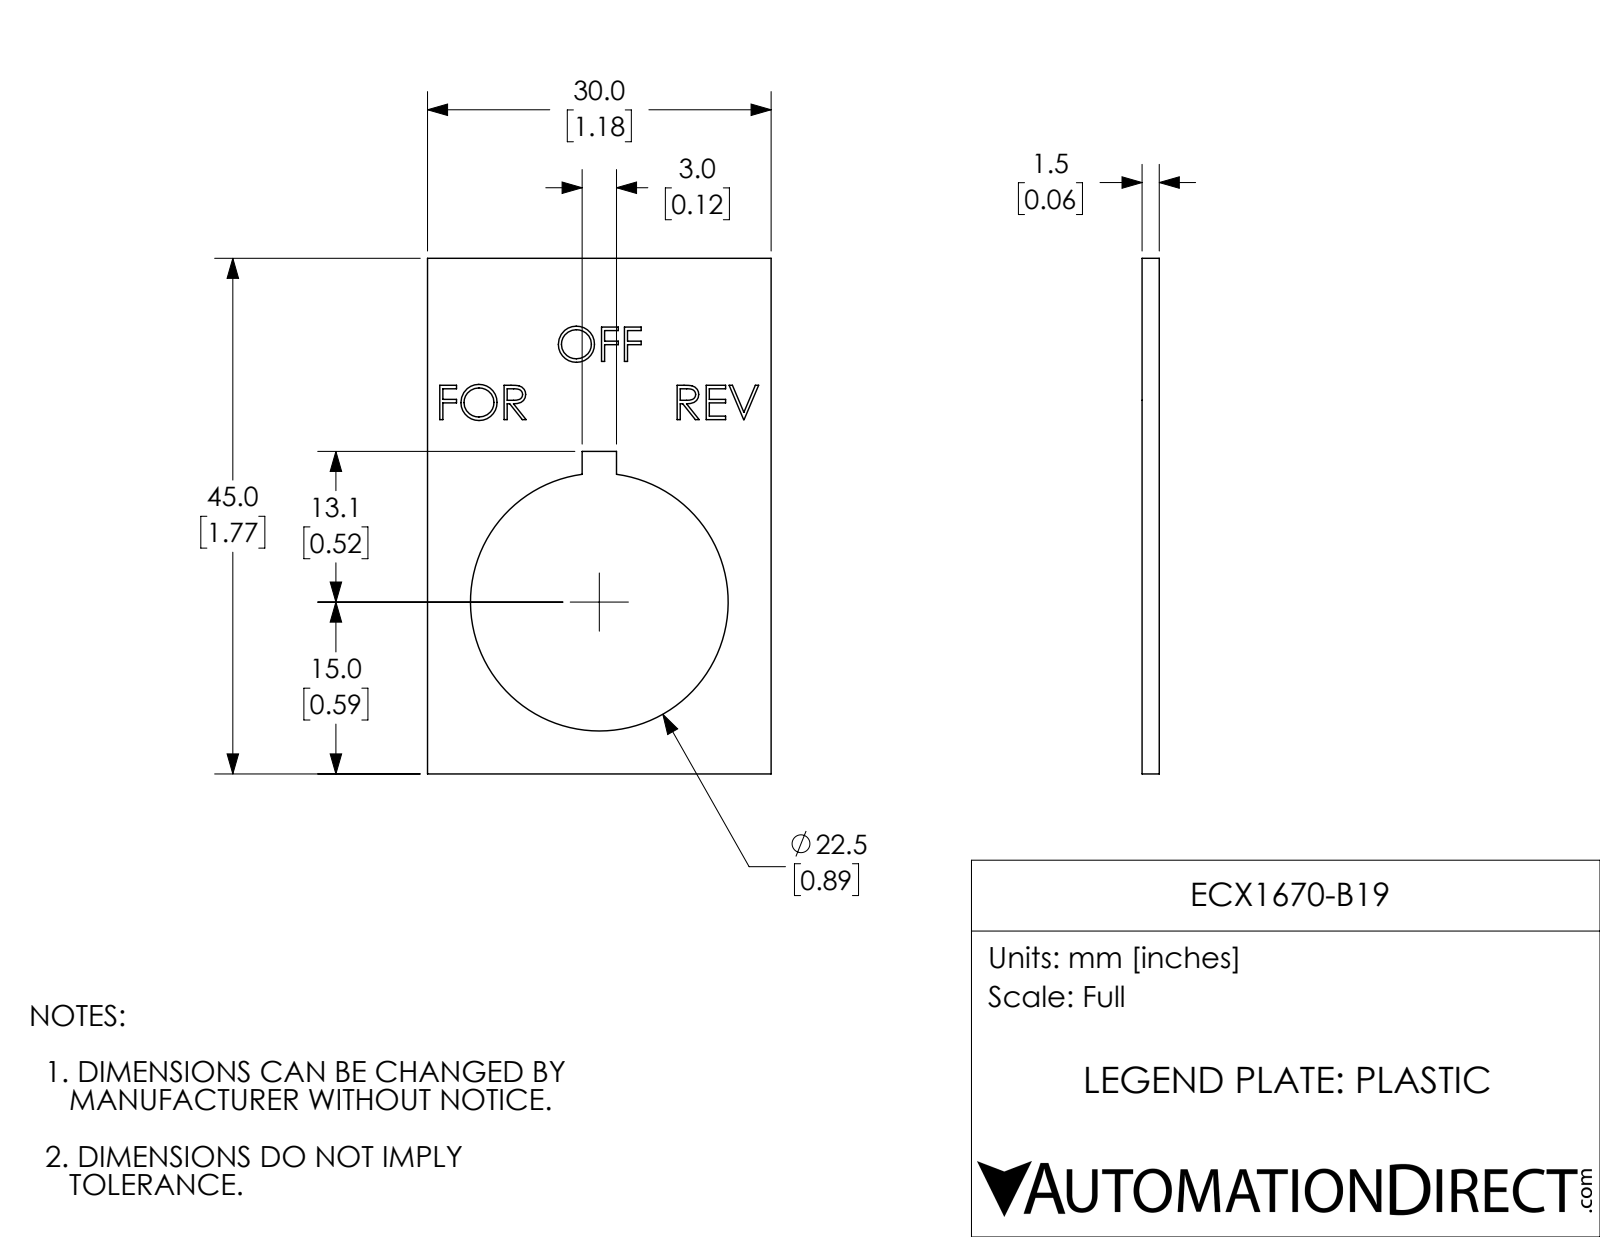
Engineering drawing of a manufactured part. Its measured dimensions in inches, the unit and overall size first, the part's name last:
Units: inches
Overall size (bounding box): 1.772 × 1.181 × 0.059
Round holes (diameter × count): ⌀0.886 ×1
Main face-to-face distances: 0.059, 1.181, 1.772, 0.058, 0.531, 0.65, 1.108, 0.663, 0.118, 0.012
Volume: 0.087 in³ · Surface area: 3.462 in²
Bodies: 1 solid, 122 faces (93 planar, 3 cylindrical, 26 other)
Part name (STEP PRODUCT): ECX1670-B19
STEP written by: SolidWorks 2017 (AUTOMOTIVE_DESIGN)
